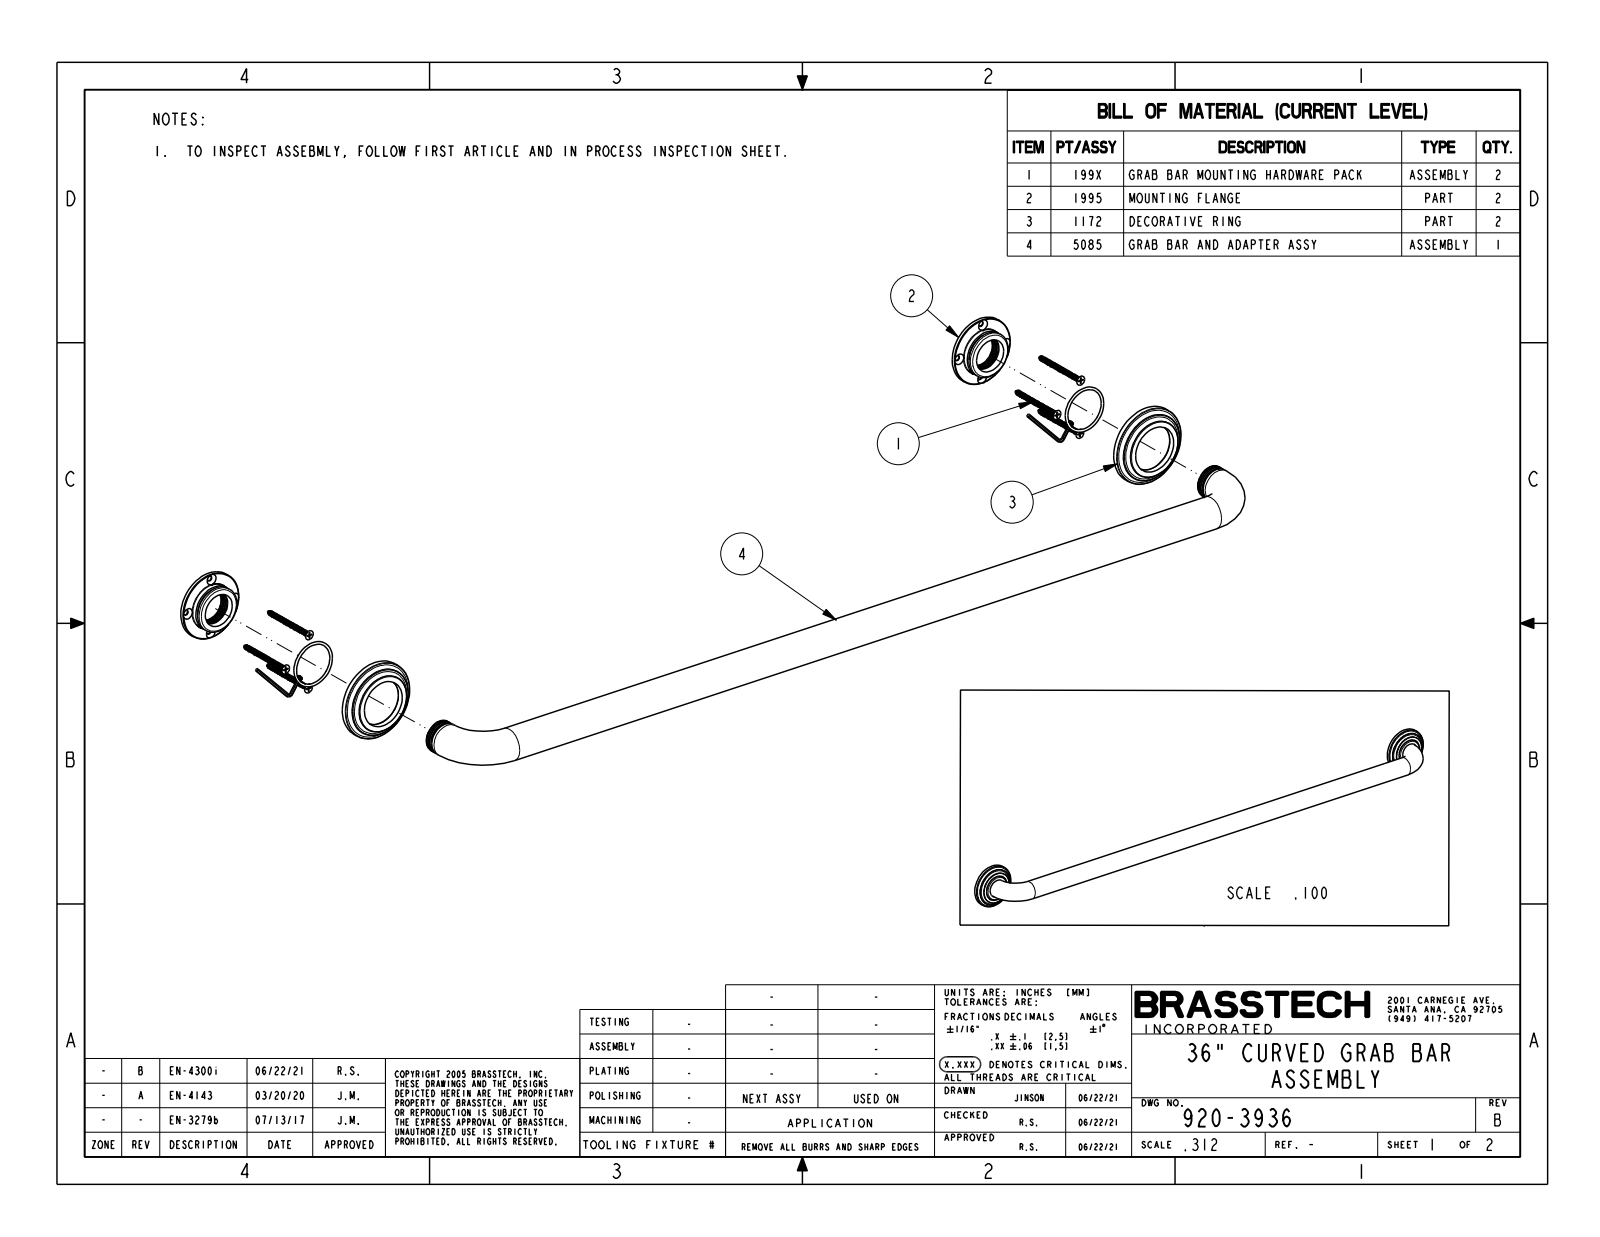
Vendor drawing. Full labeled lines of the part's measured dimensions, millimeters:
Part name (STEP PRODUCT): 1995; 20-287_ASM; 80531; 50869 (+3 more)
STEP written by: PRO/ENGINEER BY PARAMETRIC TECHNOLOGY CORPORATION, 2013150 (CONFIG_CONTROL_DESIGN)
Units: millimetres
Bodies: 7 solids, 676 faces (160 planar, 204 cylindrical, 312 other)
Overall size (bounding box): 990.6 × 76.2 × 69.9
Volume: 179 600 mm³ · Surface area: 348 600 mm²
Round holes (diameter × count): ⌀5.1 ×8, ⌀29.3 ×3, ⌀4.1 ×2, ⌀22 ×2, ⌀29.5 ×2, ⌀32 ×2, ⌀45 ×2, ⌀72.2 ×2
Round bosses / shafts (diameter × count): ⌀31.8 ×3, ⌀76.2 ×2, ⌀66 ×2, ⌀55.9 ×2, ⌀49 ×2, ⌀44.5 ×2, ⌀40.5 ×2, ⌀31.4 ×2
Partial cylindrical surfaces — rounded edges, fillets, slot ends (radius × count): R5.4 ×8, R1 ×2
Main face-to-face distances: 3.8, 9.5, 13.3, 1.9, 11.4, 4.2, 15.2, 8.9, 2.5, 6.1
Hole centre spacings: 27.6, 39.1, 914.4, 55.2, 887.2, 914.8, 942.4, 886.8
